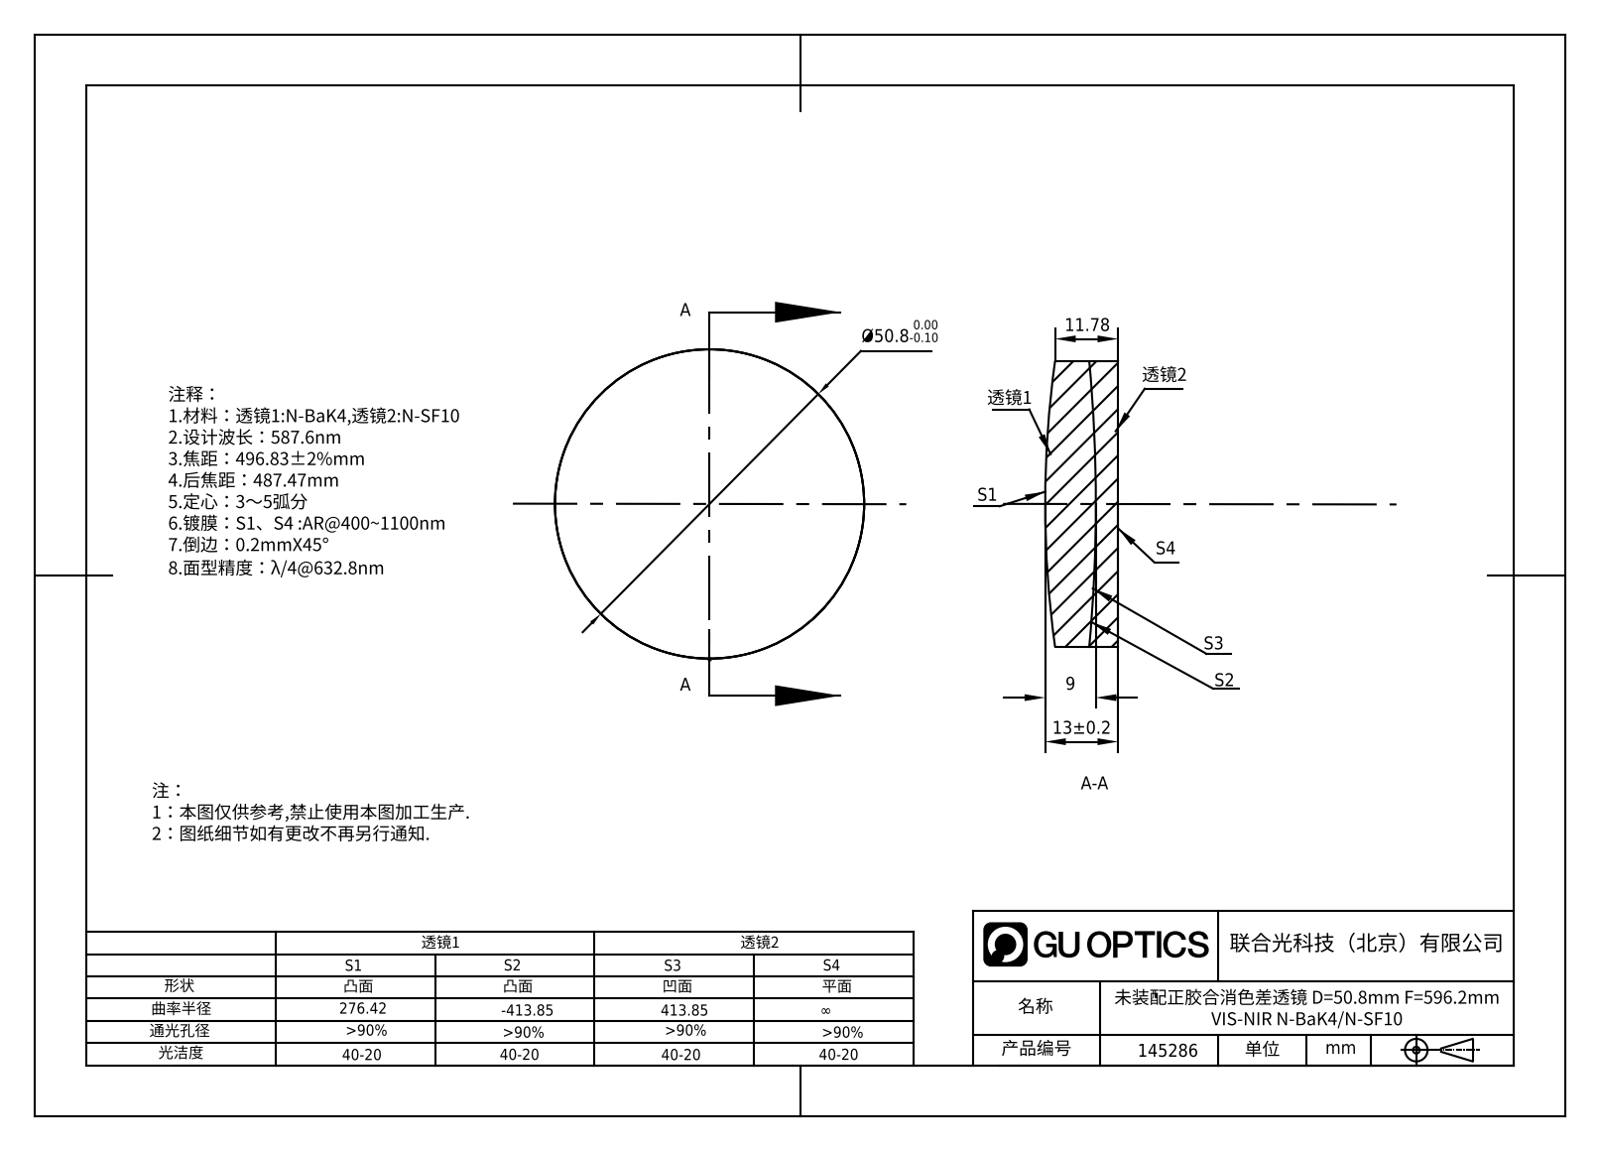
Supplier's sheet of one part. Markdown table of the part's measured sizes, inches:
| quantity | value |
| --- | --- |
| part name | 145286 |
| STEP written by | SolidWorks 2020 (CONFIG_CONTROL_DESIGN) |
| units | inches |
| bodies | 2 solids, 11 faces (1 planar, 4 cylindrical, 6 other) |
| overall size | 2 × 2 × 0.496 |
| volume | 1.511 in³ |
| surface area | 15.41 in² |
| round bosses / shafts (diameter × count) | 2 × 1 |
